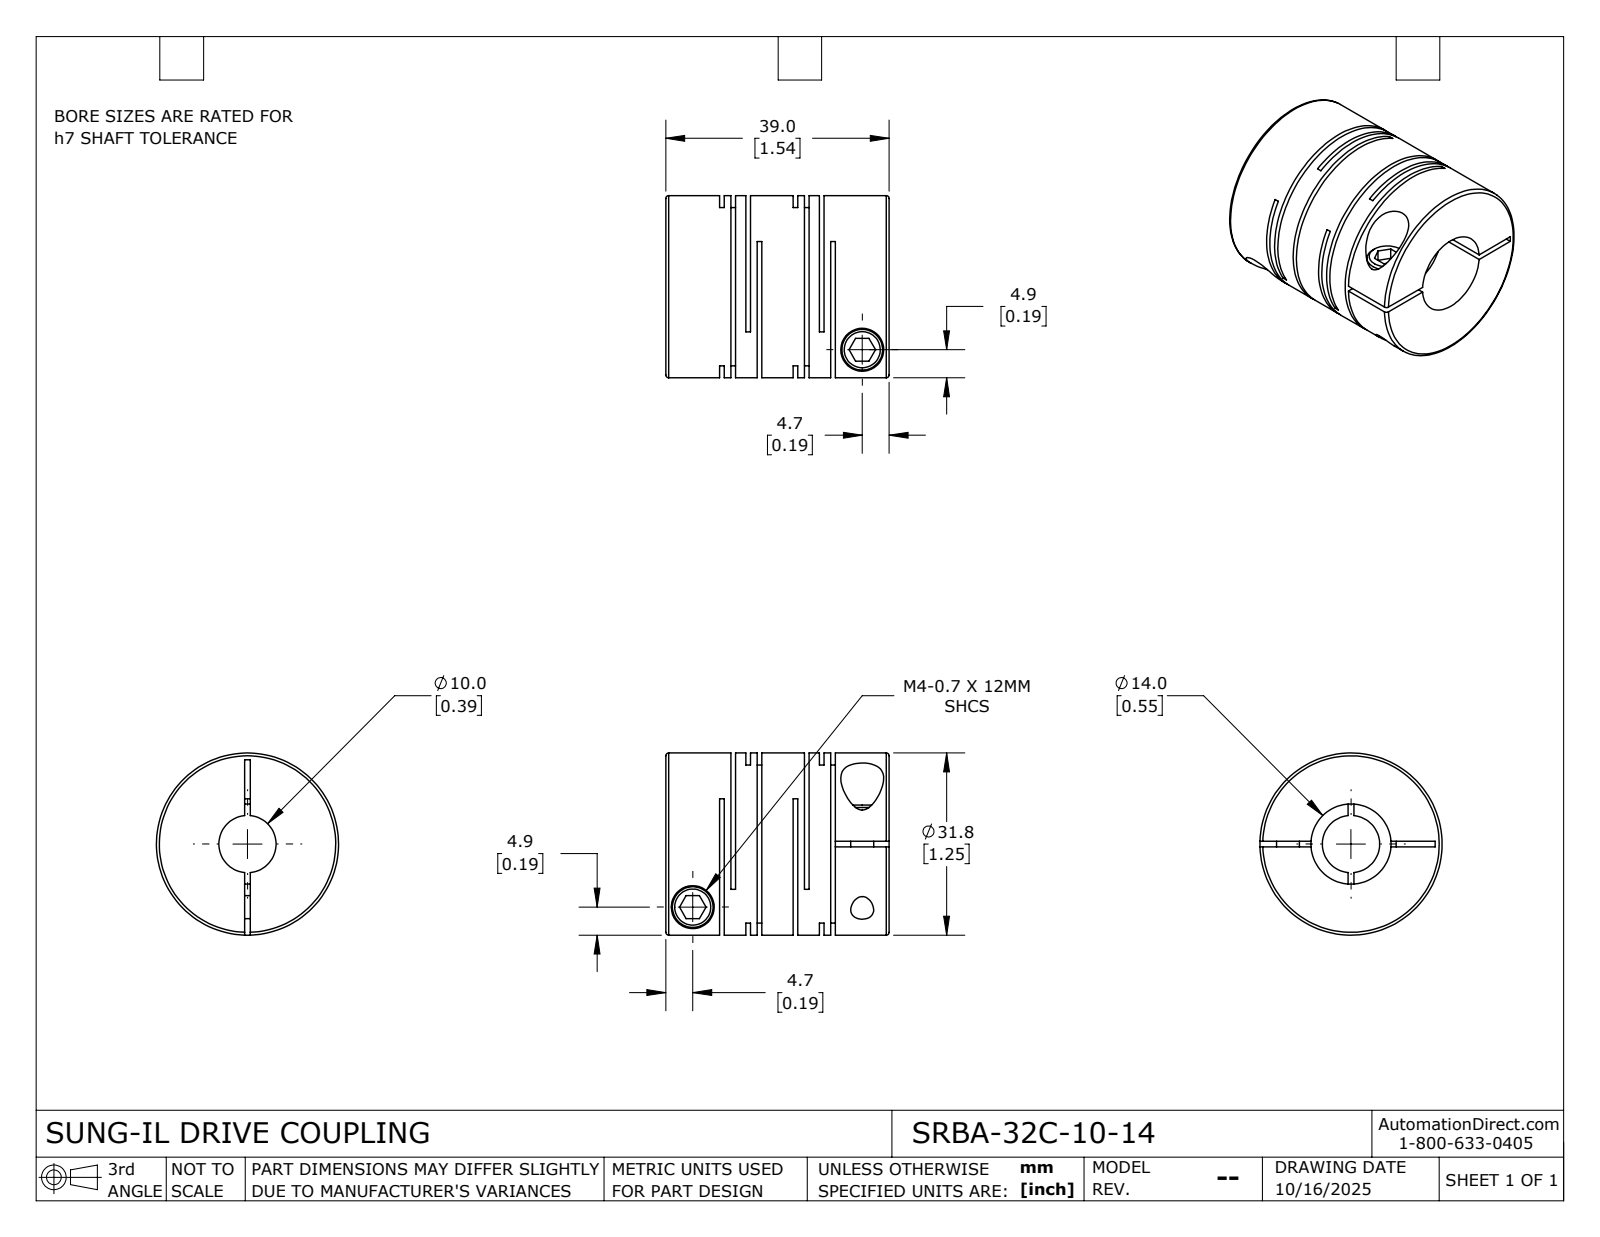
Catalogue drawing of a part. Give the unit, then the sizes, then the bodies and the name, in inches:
Units: inches
Overall size (bounding box): 1.535 × 1.252 × 1.252
Round holes (diameter × count): ⌀0.157 ×2, ⌀0.295 ×2, ⌀0.394 ×1, ⌀0.551 ×1
Round bosses / shafts (diameter × count): ⌀0.28 ×2, ⌀1.252 ×1
Main face-to-face distances: 0.031, 0.506, 0.078, 0.18, 0.474, 0.046, 0.428, 0.149, 0.325, 0.102
Volume: 1.325 in³ · Surface area: 23.6 in²
Bodies: 1 solid, 115 faces (60 planar, 42 cylindrical, 13 other)
Part name (STEP PRODUCT): SRBA-32C-10-14
STEP written by: SolidWorks 2024 (CONFIG_CONTROL_DESIGN)
